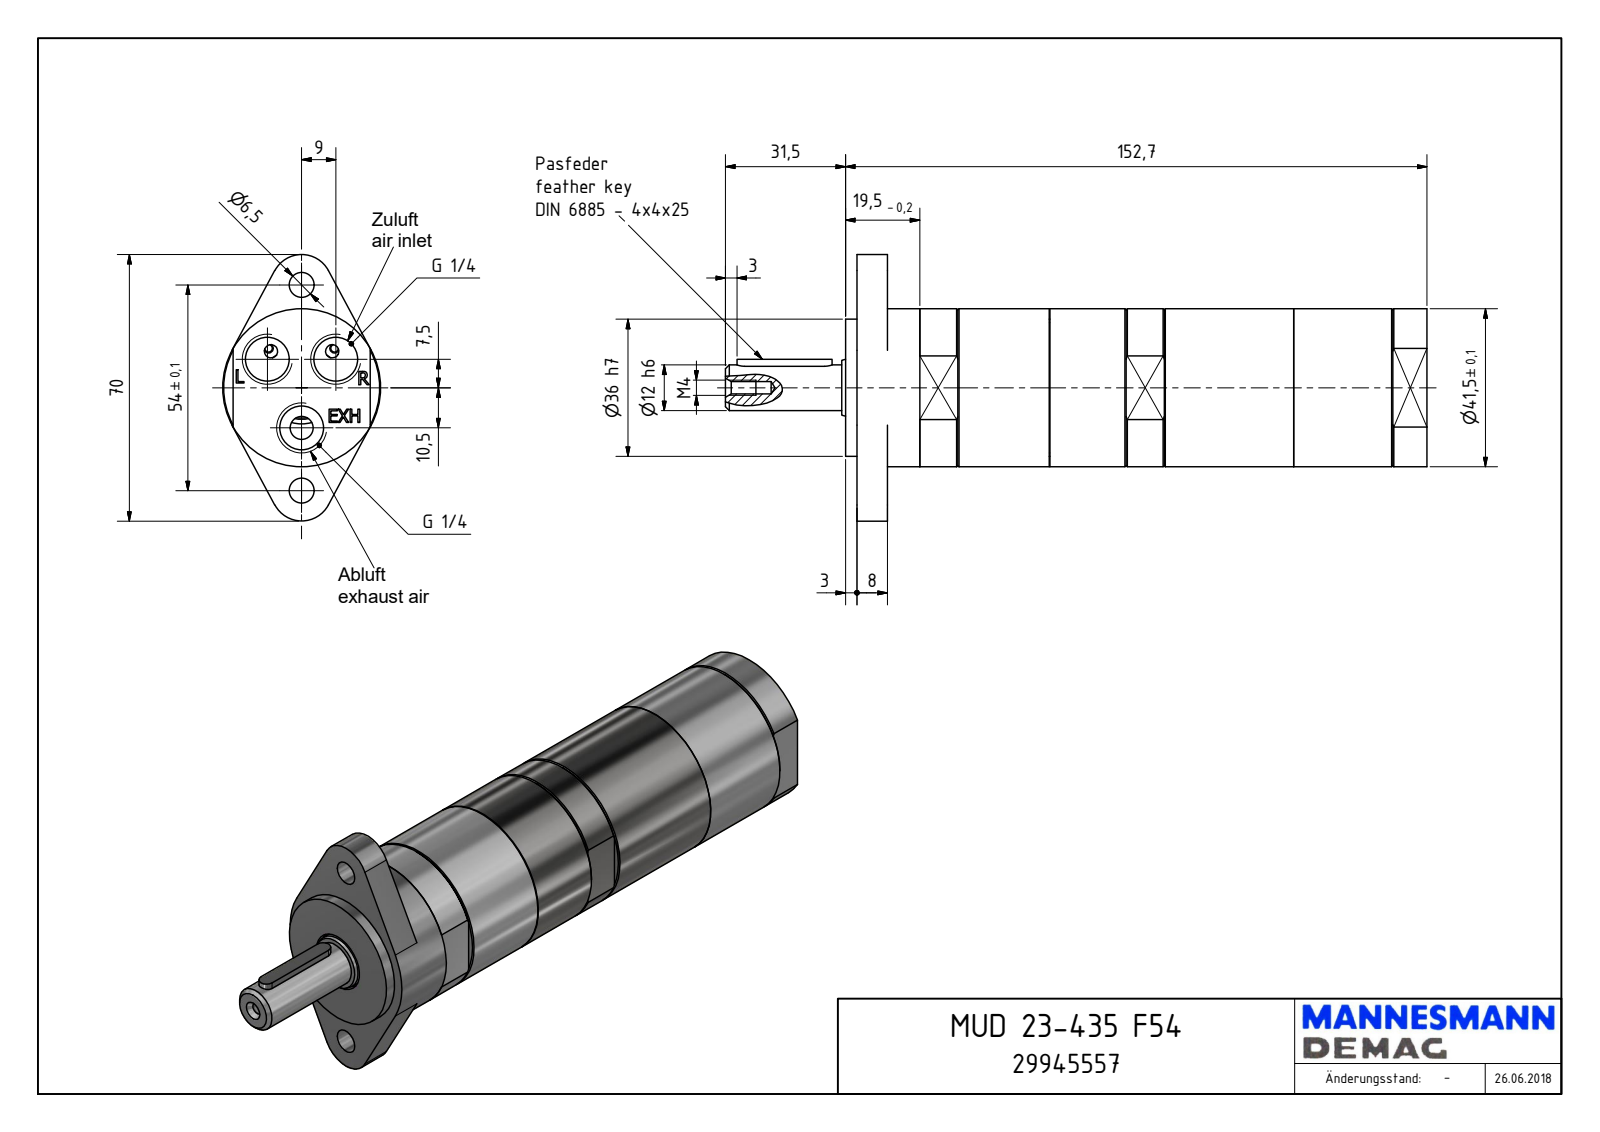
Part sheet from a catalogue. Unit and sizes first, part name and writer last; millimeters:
Units: millimetres
Overall size (bounding box): 184.2 × 70 × 41.5
Round holes (diameter × count): ⌀11.45 ×3, ⌀6.5 ×2, ⌀3.24 ×1, ⌀16 ×1, ⌀23 ×1
Round bosses / shafts (diameter × count): ⌀41.5 ×1, ⌀36 ×1, ⌀14.95 ×1, ⌀12 ×1
Partial cylindrical surfaces — rounded edges, fillets, slot ends (radius × count): R2 ×2, R8 ×2
Main face-to-face distances: 3, 149.7, 152.7, 141.7, 11, 8, 1, 42.5, 41.48, 37
Hole centre spacings: 11.72, 20.12, 21.48, 27, 35.65, 10.5, 16.5, 18
Volume: 208 610 mm³ · Surface area: 27 798 mm²
Bodies: 1 solid, 153 faces (98 planar, 27 cylindrical, 28 other)
Part name (STEP PRODUCT): MUD 23-435 F54_29945557
STEP written by: Autodesk Inventor 2018 (AUTOMOTIVE_DESIGN)
